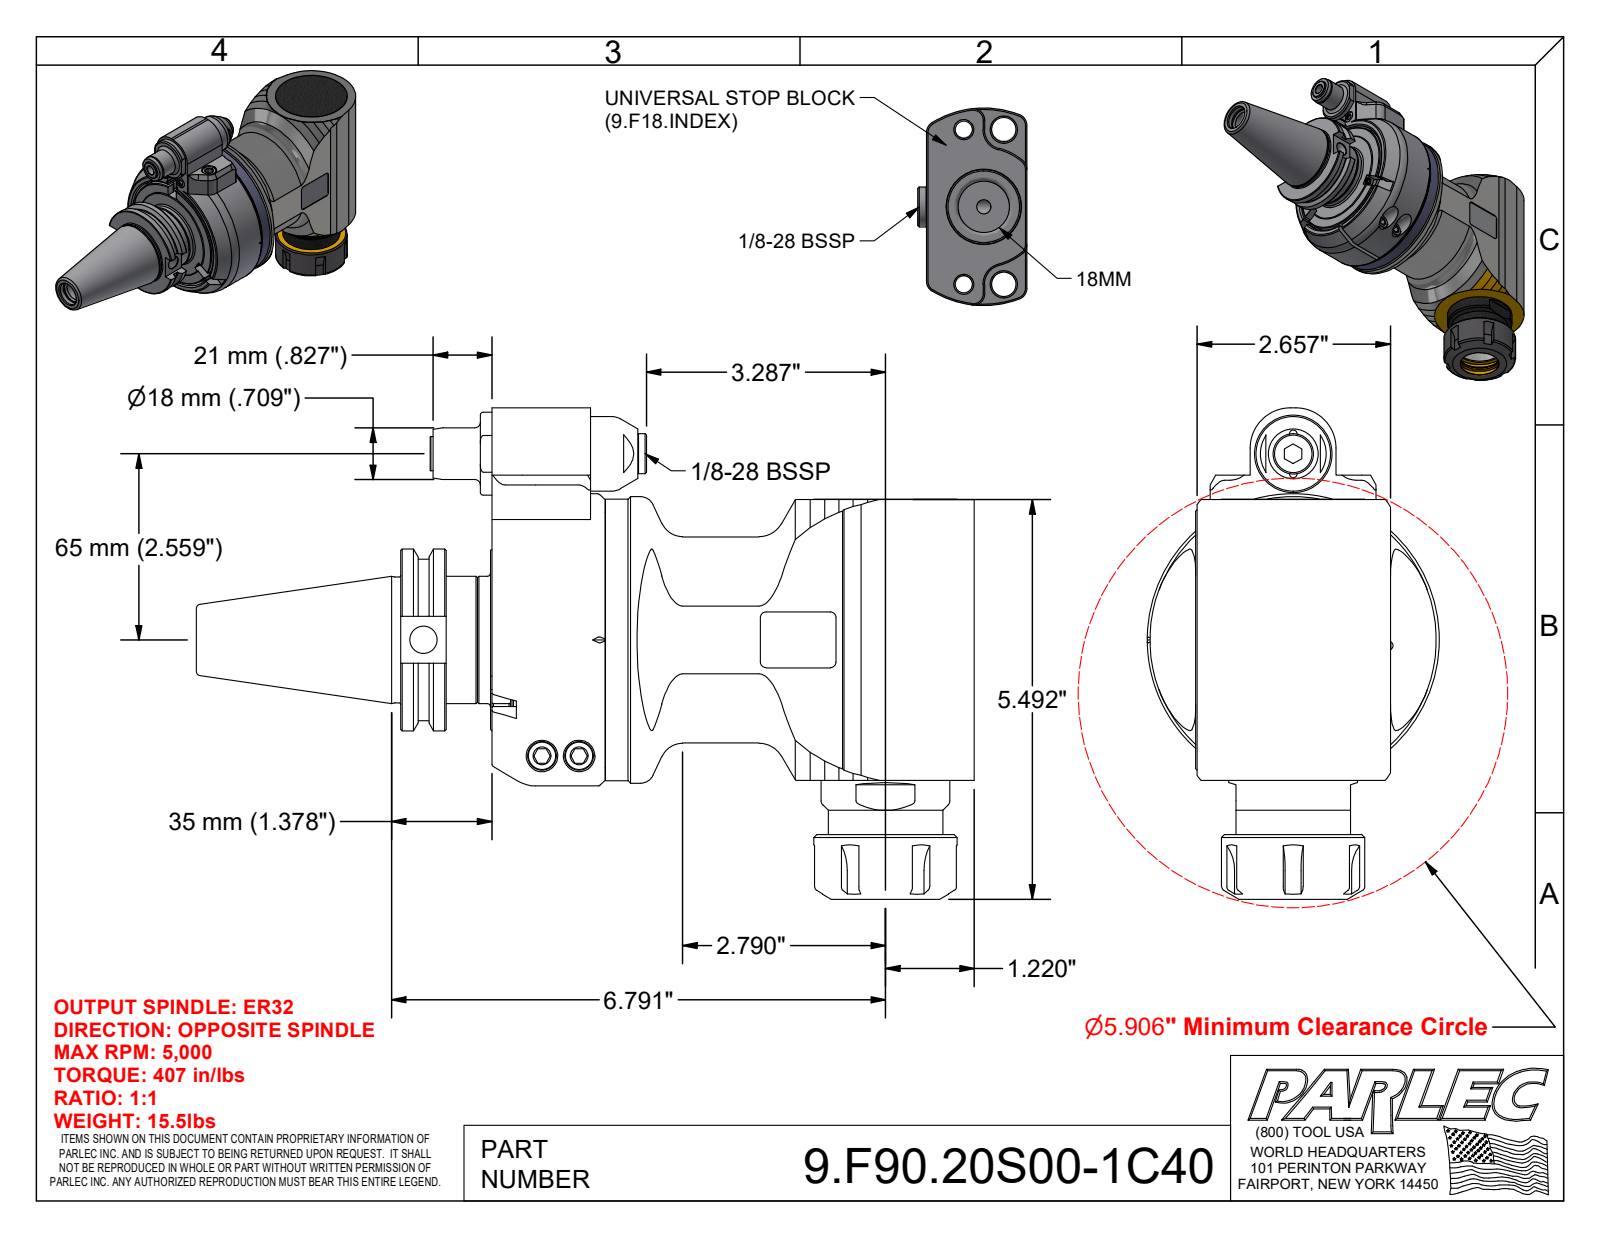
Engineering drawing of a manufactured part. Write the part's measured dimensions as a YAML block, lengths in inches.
part_name: "9.F90.20S00-1C40; 9.F90.20S00; 9_GA1_446_2 (EVO, Type 1, C40, 65mm, 35mm)"
step_written_by: "Autodesk Inventor 2022 (AUTOMOTIVE_DESIGN)"
units: inches
bodies: {solids: 6, faces: 664, planar: 294, cylindrical: 161, other: 209}
overall_size: [10.699, 6.752, 4.016]
volume: 21.83
surface_area: 254.3
round_holes:
  - {diameter: 0.126, count: 4}
  - {diameter: 0.197, count: 3}
  - {diameter: 0.256, count: 3}
  - {diameter: 0.492, count: 3}
  - {diameter: 0.102, count: 2}
  - {diameter: 0.13, count: 2}
  - {diameter: 0.165, count: 2}
  - {diameter: 0.315, count: 2}
  - {diameter: 0.409, count: 2}
  - {diameter: 0.433, count: 2}
  - {diameter: 1.063, count: 2}
  - {diameter: 0.098, count: 1}
round_bosses_or_shafts:
  - {diameter: 0.394, count: 4}
  - {diameter: 0.472, count: 3}
  - {diameter: 1.575, count: 2}
  - {diameter: 0.709, count: 2}
  - {diameter: 0.236, count: 2}
  - {diameter: 0.098, count: 2}
  - {diameter: 4.016, count: 1}
  - {diameter: 3.937, count: 1}
partial_cylinders:
  - {radius: 0.039, count: 14}
  - {radius: 0.079, count: 12}
  - {radius: 0.118, count: 6}
  - {radius: 0.591, count: 6}
  - {radius: 0.157, count: 4}
  - {radius: 0.02, count: 2}
  - {radius: 0.315, count: 2}
  - {radius: 0.551, count: 2}
face_to_face_distances: [0.02, 0.039, 0.276, 1.26, 0.295, 0.335, 1.28, 1.555, 0.059, 2.677]
hole_center_spacings: [0.325, 0.459, 0.276, 0.504, 0.65, 0.74, 0.996, 1.596]
